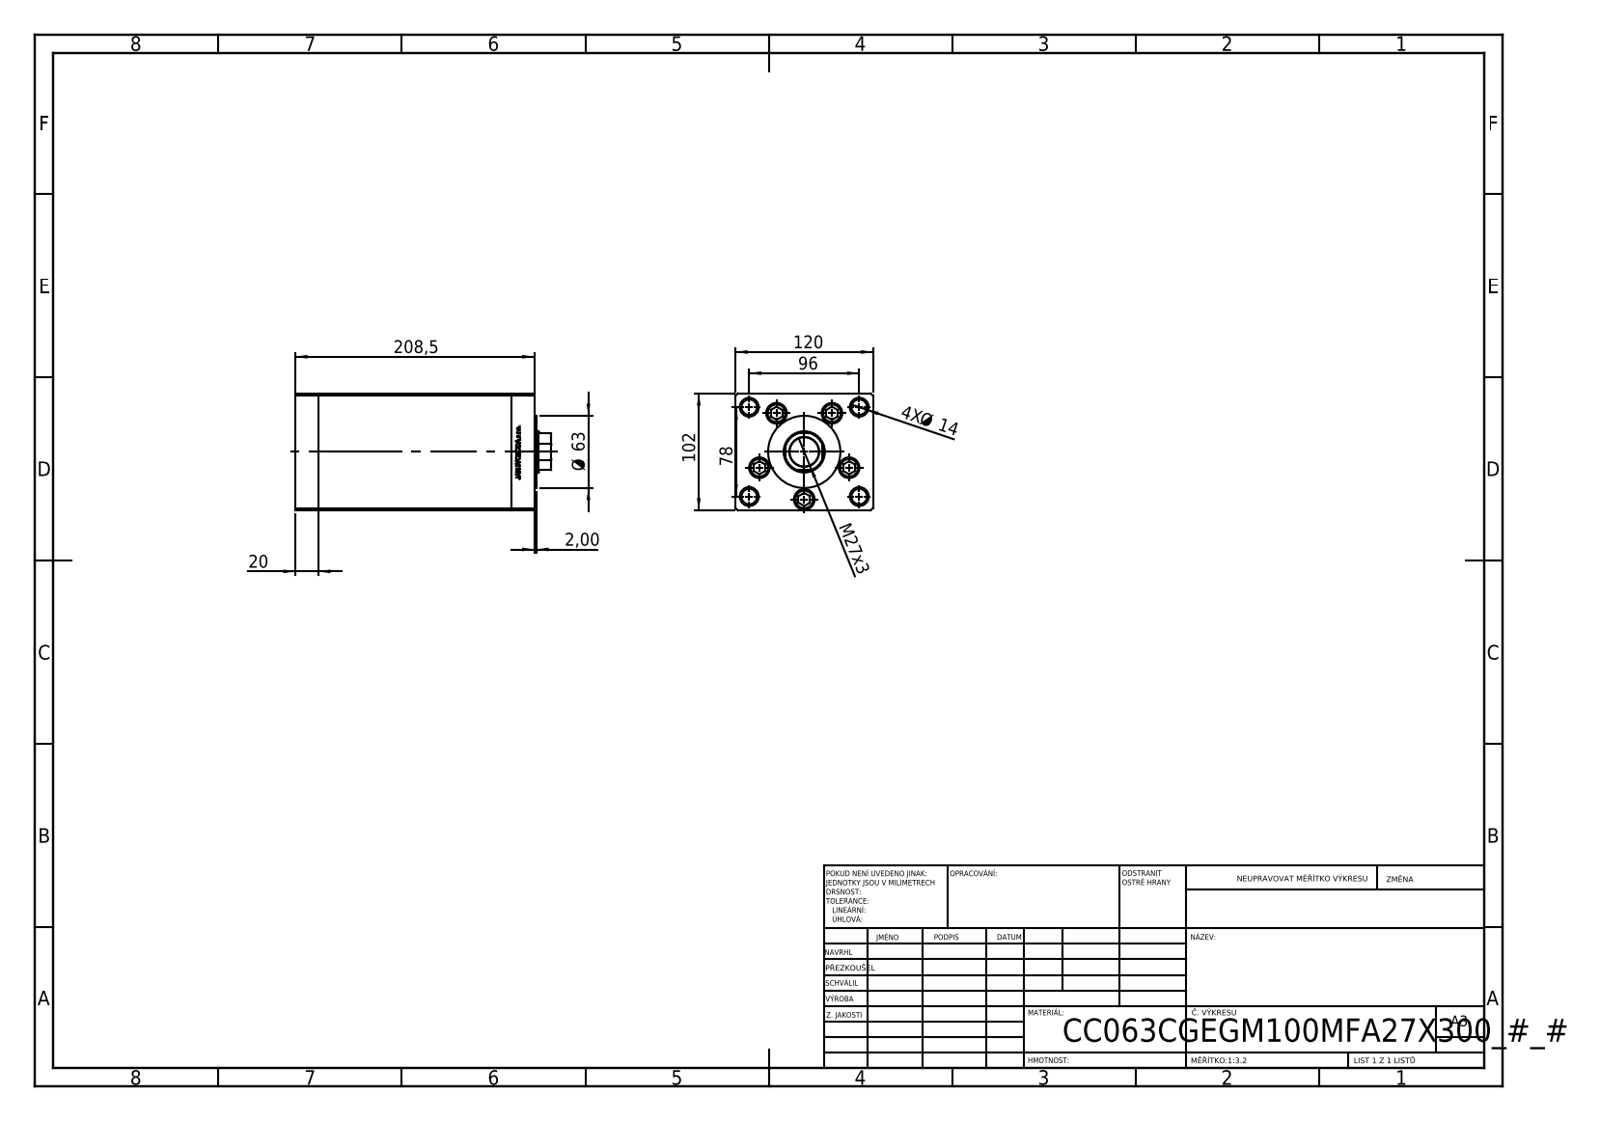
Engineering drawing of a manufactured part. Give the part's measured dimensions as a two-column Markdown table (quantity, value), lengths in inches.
| quantity | value |
| --- | --- |
| part name | V220C FRONT; ALLEN BOLT; V220C_C MIDDLE; V220C_VC_C (+1 more) |
| STEP written by | SolidWorks 2019 (CONFIG_CONTROL_DESIGN) |
| units | inches |
| bodies | 13 solids, 1165 faces (542 planar, 161 cylindrical, 462 other) |
| overall size | 8.799 × 4.724 × 4.016 |
| volume | 130.7 in³ |
| surface area | 462.6 in² |
| round holes (diameter × count) | 0.531 × 9, 0.709 × 5, 0.472 × 4, 0.65 × 4, 0.669 × 1, 1.004 × 1, 1.417 × 1 |
| round bosses / shafts (diameter × count) | 0.315 × 5, 0.669 × 4, 2.48 × 1 |
| partial cylindrical surfaces (radius × count) | 0.037 × 2, 0.689 × 1 |
| main face-to-face distances | 4.724, 4.016, 0.787, 6.634, 7.421, 1.348, 8.209, 6.86, 6.073, 0.561 |
| hole center spacings | 1.634, 2.435, 0.96, 1.051, 1.887, 1.893, 1.962, 2.109 |
